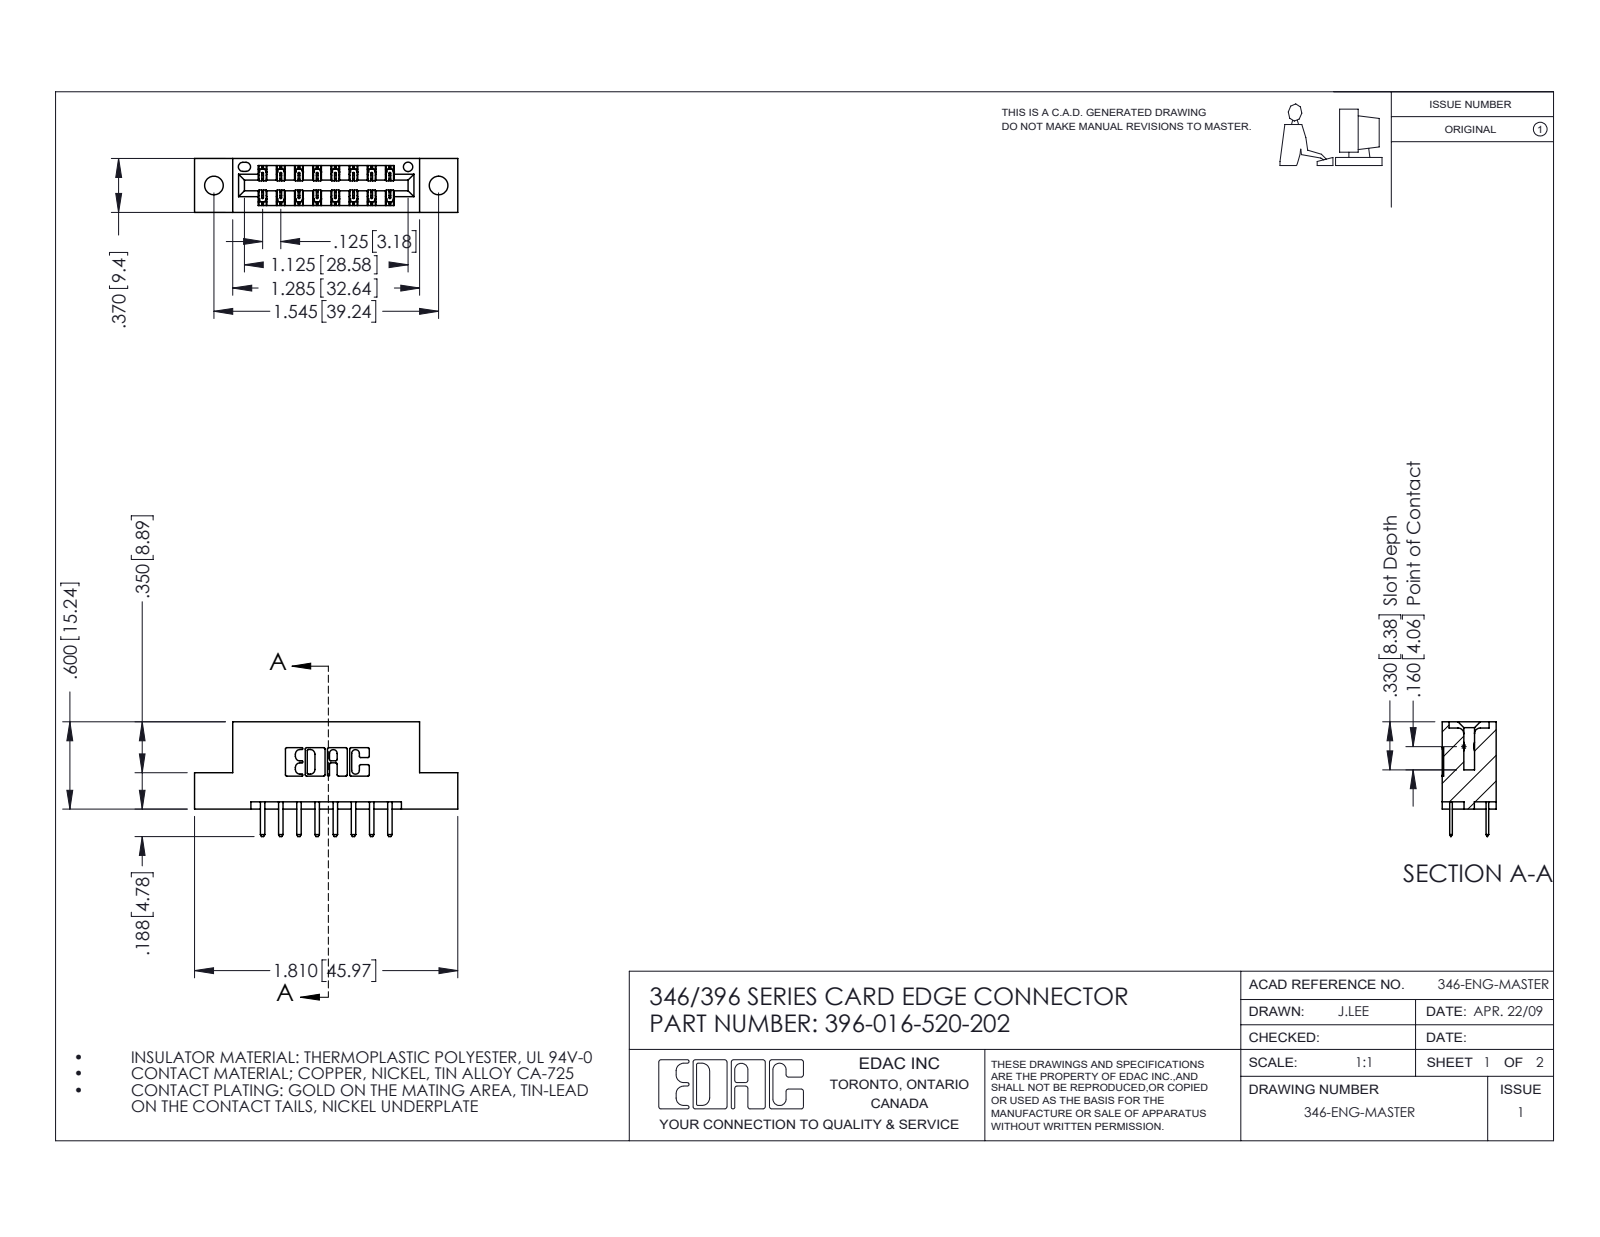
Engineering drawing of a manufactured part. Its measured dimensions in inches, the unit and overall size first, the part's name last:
Units: inches
Overall size (bounding box): 1.81 × 0.788 × 0.37
Round holes (diameter × count): ⌀0.128 ×2, ⌀0.064 ×1
Partial cylindrical surfaces — rounded edges, fillets, slot ends (radius × count): R0.006 ×24, R0.01 ×22, R0.01 ×20, R0.007 ×6, R0.031 ×6, R0.026 ×3, R0.014 ×2, R0.022 ×2
Main face-to-face distances: 0.25, 0.37, 0.048, 0.322, 0.5, 0.148, 0.222, 0.1, 0.174, 0.125
Hole centre spacings: 0.246, 1.341, 1.545
Volume: 0.255 in³ · Surface area: 7.625 in²
Bodies: 17 solids, 1018 faces (668 planar, 350 cylindrical, 0 other)
Part name (STEP PRODUCT): 345-292-001_345-293-120; 346 Part_Flush Mounting Lugs - 0.128 Dia; 396-016-520-202
STEP written by: SolidWorks 2016 (CONFIG_CONTROL_DESIGN)
